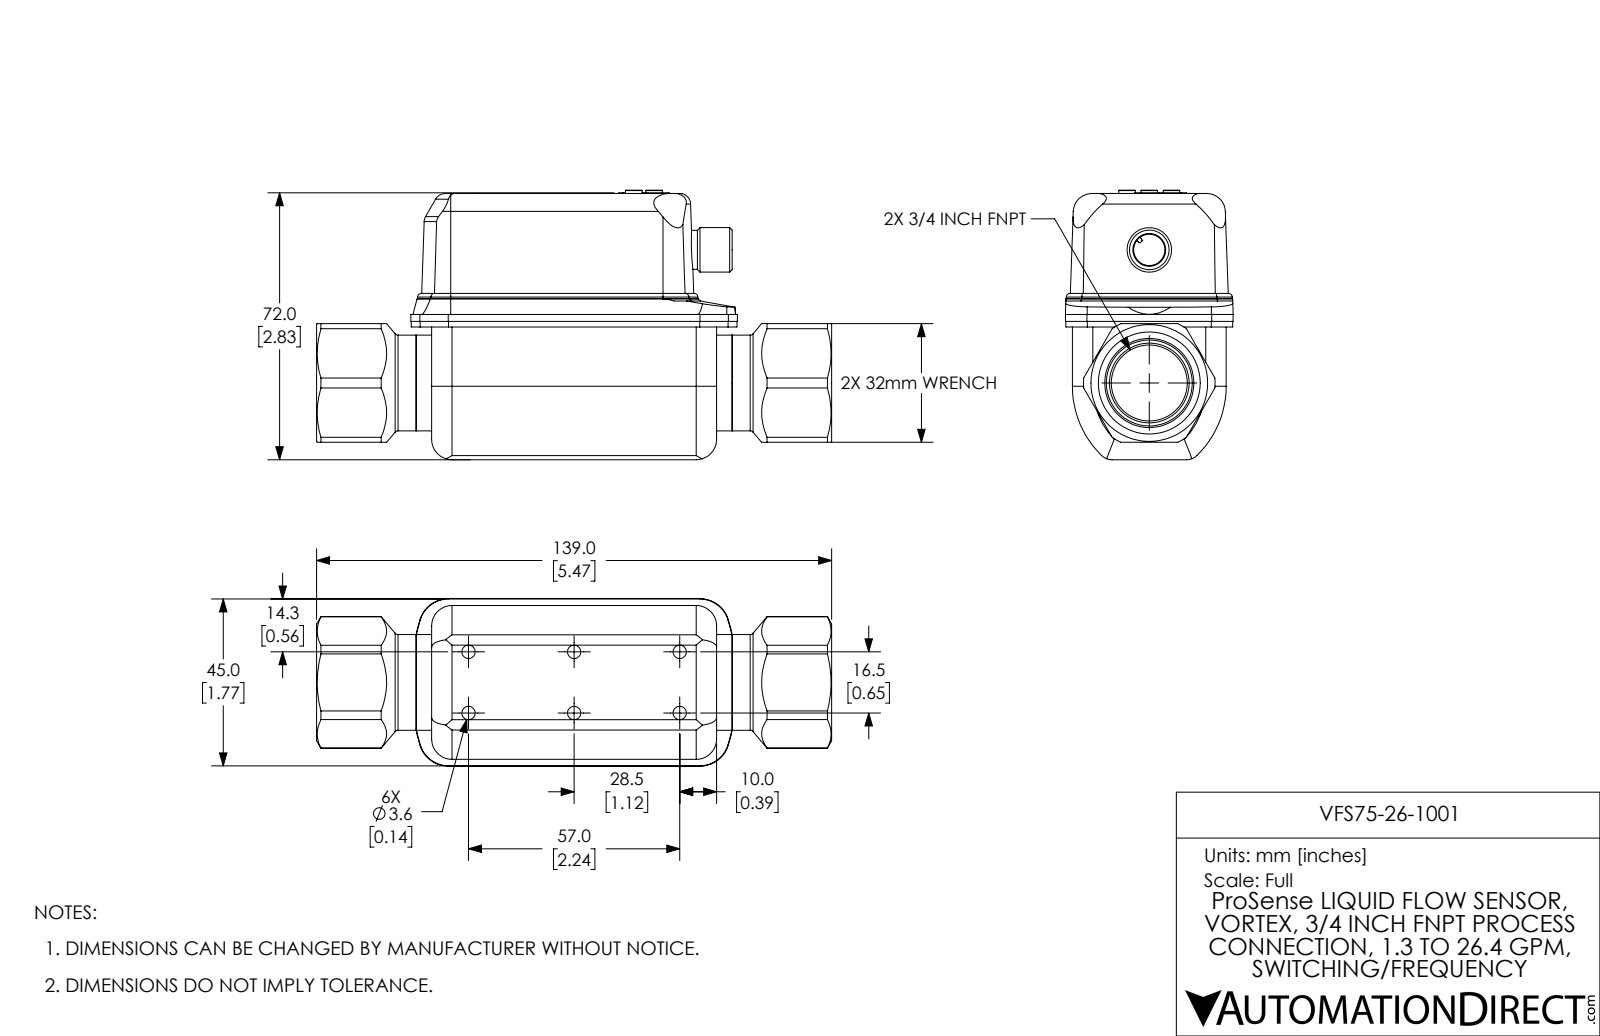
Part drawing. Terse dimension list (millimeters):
name: VFS75-26-1001
written by: SolidWorks 2017 (AUTOMOTIVE_DESIGN)
unit: mm
bodies: 1 solid, 316 faces (90 planar, 123 cylindrical, 103 other)
size: 139 × 72.7 × 45.28
volume: 235 867 mm³; area: 33 978 mm²
holes: 6× ⌀3.6, 1× ⌀0.8, 1× ⌀2.2, 1× ⌀8.45, 1× ⌀20.5, 1× ⌀26.8
bosses: 3× ⌀4.45, 1× ⌀25.8, 1× ⌀12, 1× ⌀10.5
rounds: 12× R0.2, 8× R8, 6× R5.5, 4× R0.5, 4× R4, 4× R7.89, 4× R60, 2× R0.15
face distances: 32, 71.8, 41.5, 71.75, 76.75, 36, 35.8, 35.95, 0.9, 67.05
hole spacings: 28.5, 32.93, 16.5, 57, 59.34, 12.6, 16.26, 18.89
